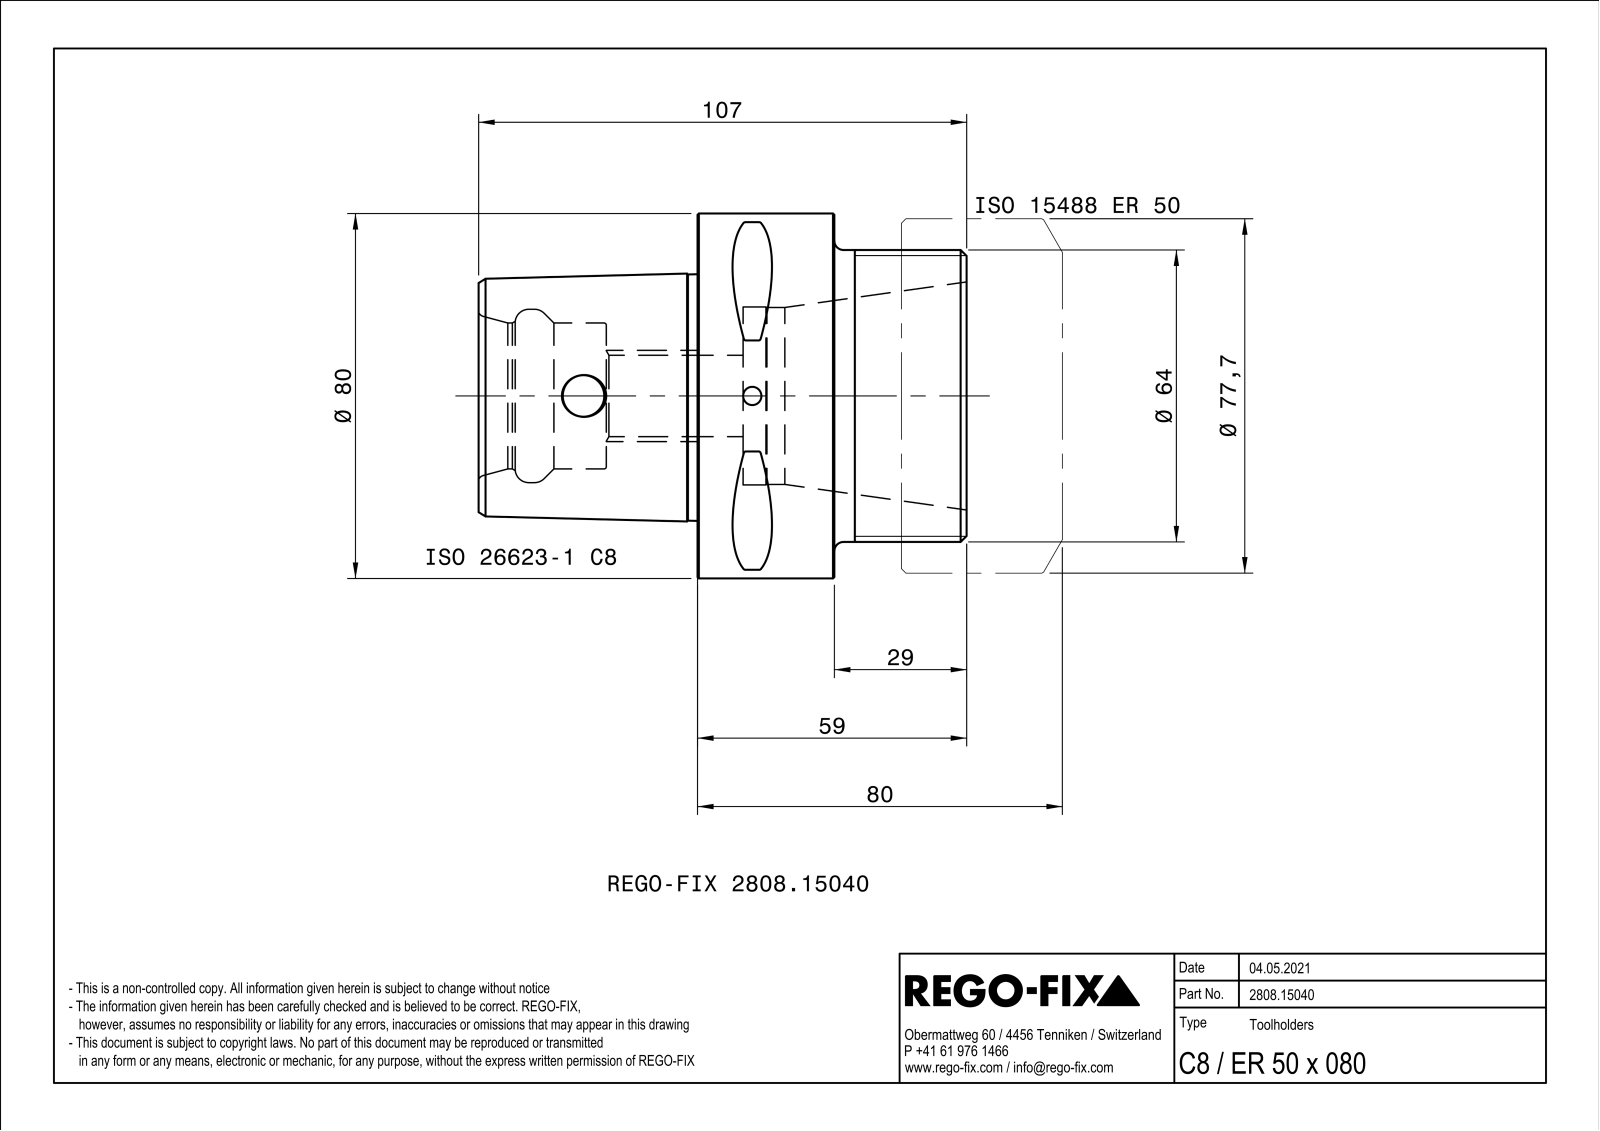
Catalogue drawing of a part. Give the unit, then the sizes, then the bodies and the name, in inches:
Units: inches
Overall size (bounding box): 4.213 × 3.15 × 3.15
Round holes (diameter × count): ⌀0.157 ×1, ⌀0.358 ×1, ⌀0.702 ×1, ⌀1.26 ×1, ⌀1.496 ×1, ⌀1.528 ×1, ⌀1.535 ×1
Round bosses / shafts (diameter × count): ⌀3.15 ×1, ⌀2.52 ×1
Partial cylindrical surfaces — rounded edges, fillets, slot ends (radius × count): R0.02 ×8, R0.236 ×1
Main face-to-face distances: 1.181, 0.787, 1.142, 2.323, 1.929, 0.394, 4.213, 3.071, 2.283, 1.89
Hole centre spacings: 1.457
Volume: 14.74 in³ · Surface area: 64.95 in²
Bodies: 1 solid, 102 faces (21 planar, 22 cylindrical, 59 other)
Part name (STEP PRODUCT): NOCUT
STEP written by: SIEMENS PLM Software Solid Edge ST10 (AUTOMOTIVE_DESIGN)
